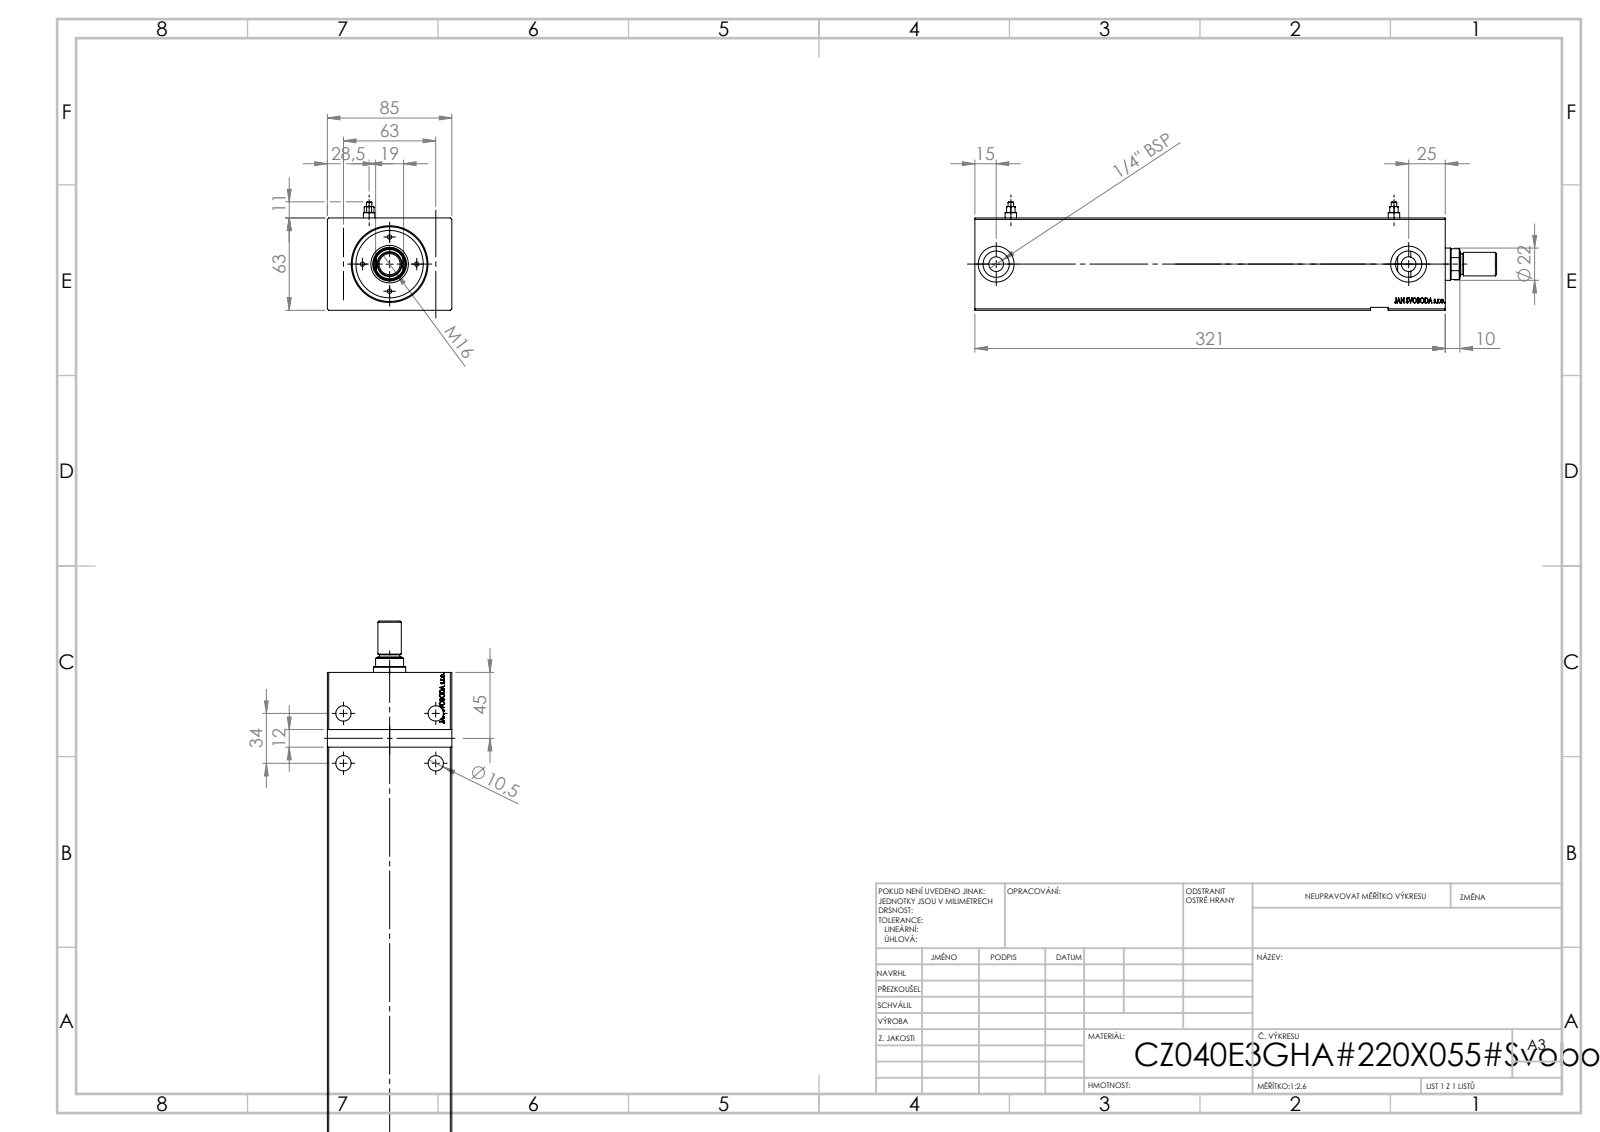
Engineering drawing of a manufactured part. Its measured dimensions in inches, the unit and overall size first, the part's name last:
Units: inches
Overall size (bounding box): 12.638 × 3.346 × 2.48
Round holes (diameter × count): ⌀0.413 ×4, ⌀0.315 ×2, ⌀0.394 ×2, ⌀0.709 ×2, ⌀0.965 ×2, ⌀1.417 ×1, ⌀1.575 ×1, ⌀2.008 ×1
Main face-to-face distances: 2.48, 3.346, 12.638, 12.035, 0.602, 0.079, 2.402, 12.63, 0.594, 4.064
Hole centre spacings: 1.339, 2.48, 2.819, 0.742, 1.267, 1.813, 2.083, 9.258
Volume: 79.03 in³ · Surface area: 237.4 in²
Bodies: 1 solid, 781 faces (384 planar, 31 cylindrical, 366 other)
STEP written by: SolidWorks 2019 (CONFIG_CONTROL_DESIGN)
